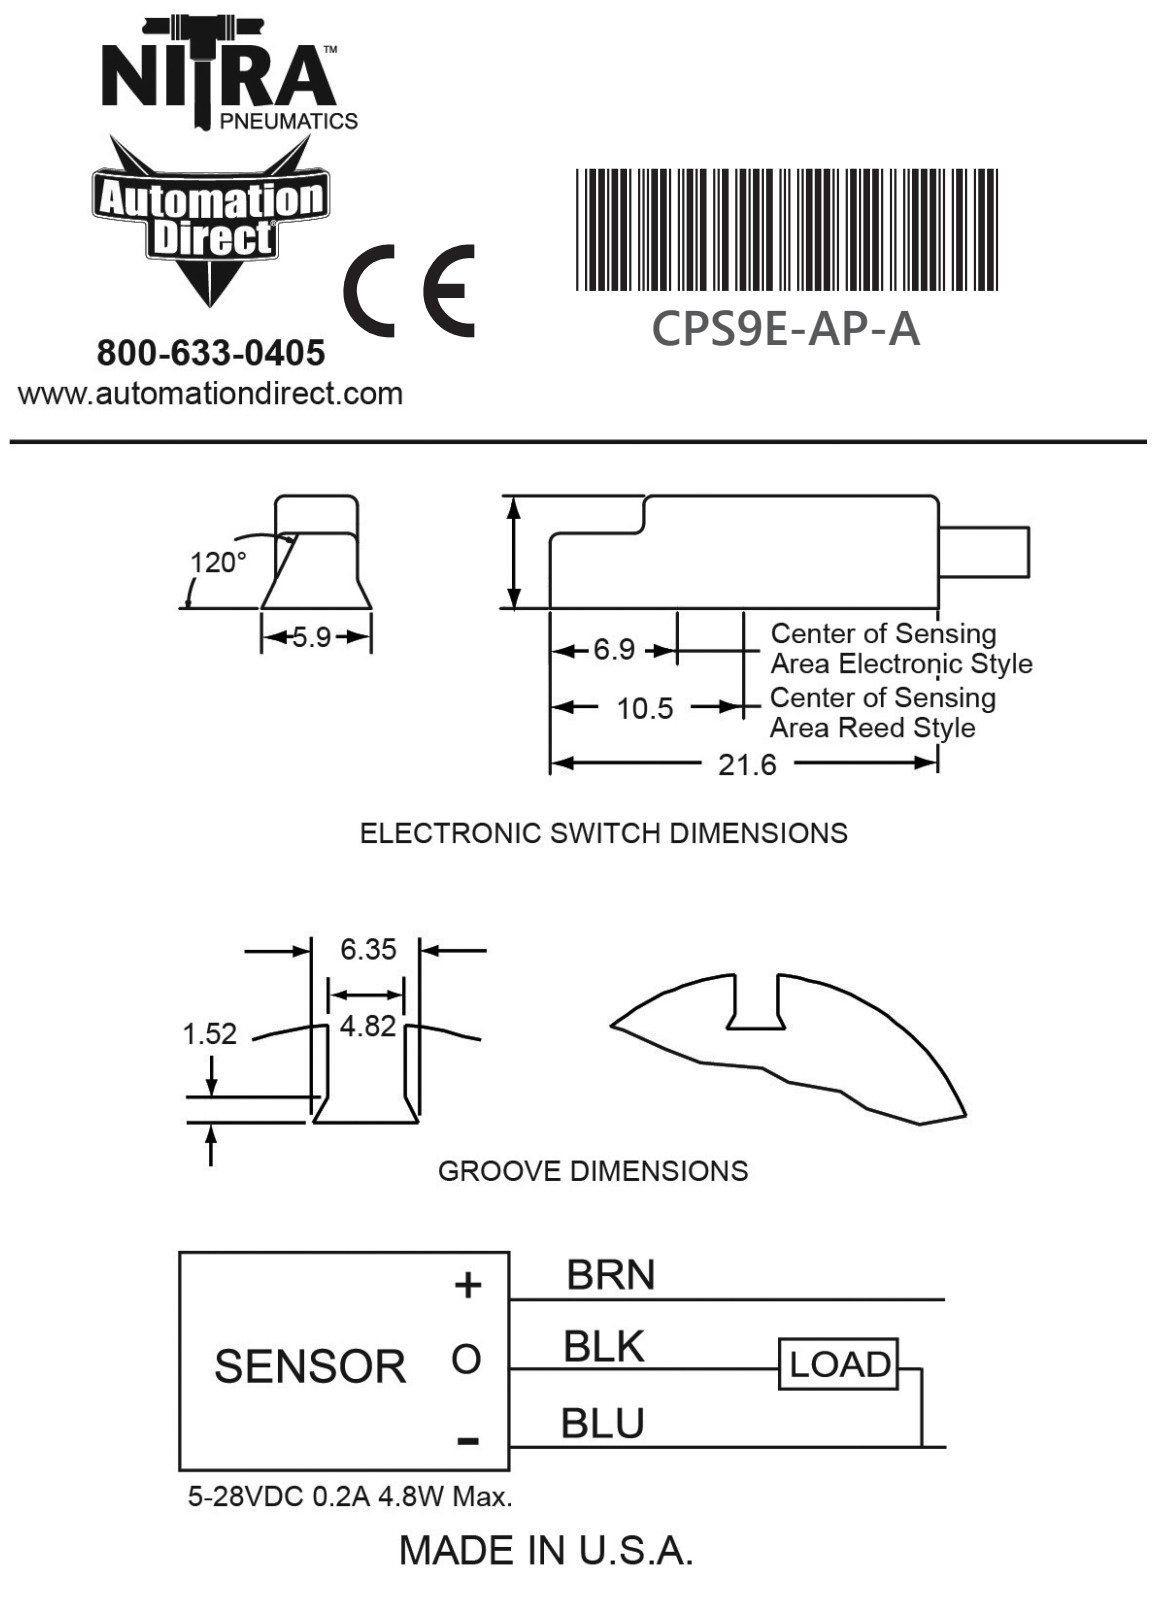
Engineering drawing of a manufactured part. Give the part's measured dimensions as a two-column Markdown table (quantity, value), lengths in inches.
| quantity | value |
| --- | --- |
| part name | CPS9E-AP-A |
| STEP written by | SolidWorks 2023 (CONFIG_CONTROL_DESIGN) |
| units | inches |
| bodies | 1 solid, 83 faces (24 planar, 41 cylindrical, 18 other) |
| overall size | 6.21 × 0.24 × 0.234 |
| volume | 0.07 in³ |
| surface area | 2.487 in² |
| round holes (diameter × count) | 0.094 × 1, 0.125 × 1 |
| round bosses / shafts (diameter × count) | 0.031 × 3, 0.016 × 3, 0.105 × 1 |
| partial cylindrical surfaces (radius × count) | 0.02 × 20 |
| main face-to-face distances | 0.175, 0.241, 0.85, 0.161, 0.08, 0.156, 0.235, 3.86, 4.71, 4.51 |
| hole center spacings | 0.172 |
